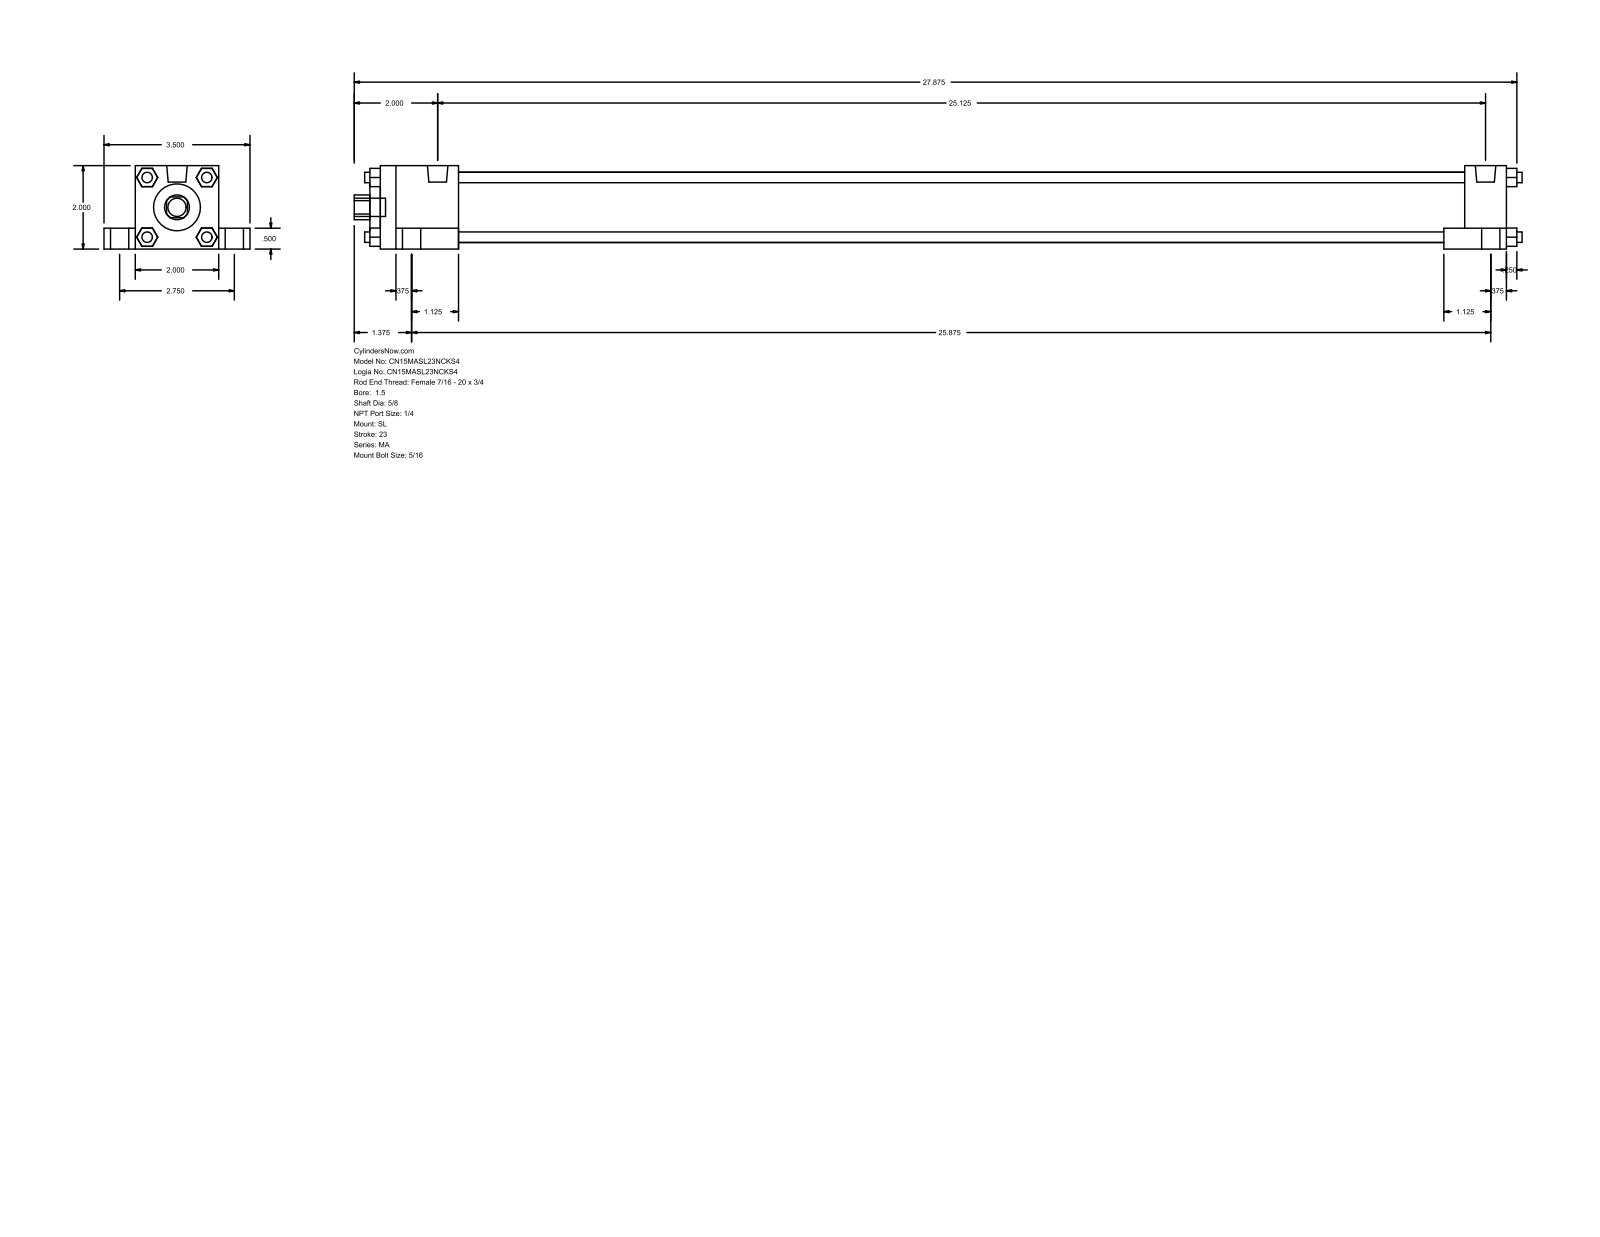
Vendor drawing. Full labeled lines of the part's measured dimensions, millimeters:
Part name (STEP PRODUCT): MA_SL__0150_0.625
STEP written by: GSSL Pune (CONFIG_CONTROL_DESIGN)
Units: millimetres
Bodies: 0 solids, 148 faces (112 planar, 36 cylindrical, 0 other)
Overall size (bounding box): 711.2 × 88.9 × 50.8
Round holes (diameter × count): ⌀15.88 ×1, ⌀28.57 ×1, ⌀42.93 ×1
Round bosses / shafts (diameter × count): ⌀11.11 ×5, ⌀17.46 ×4, ⌀7.94 ×4, ⌀6.35 ×4, ⌀12.49 ×2
Partial cylindrical surfaces — rounded edges, fillets, slot ends (radius × count): R7.54 ×1
Main face-to-face distances: 50.8, 19.05, 38.1, 12.7, 69.85, 685.79, 612.77, 6.35, 9.52, 25.4
